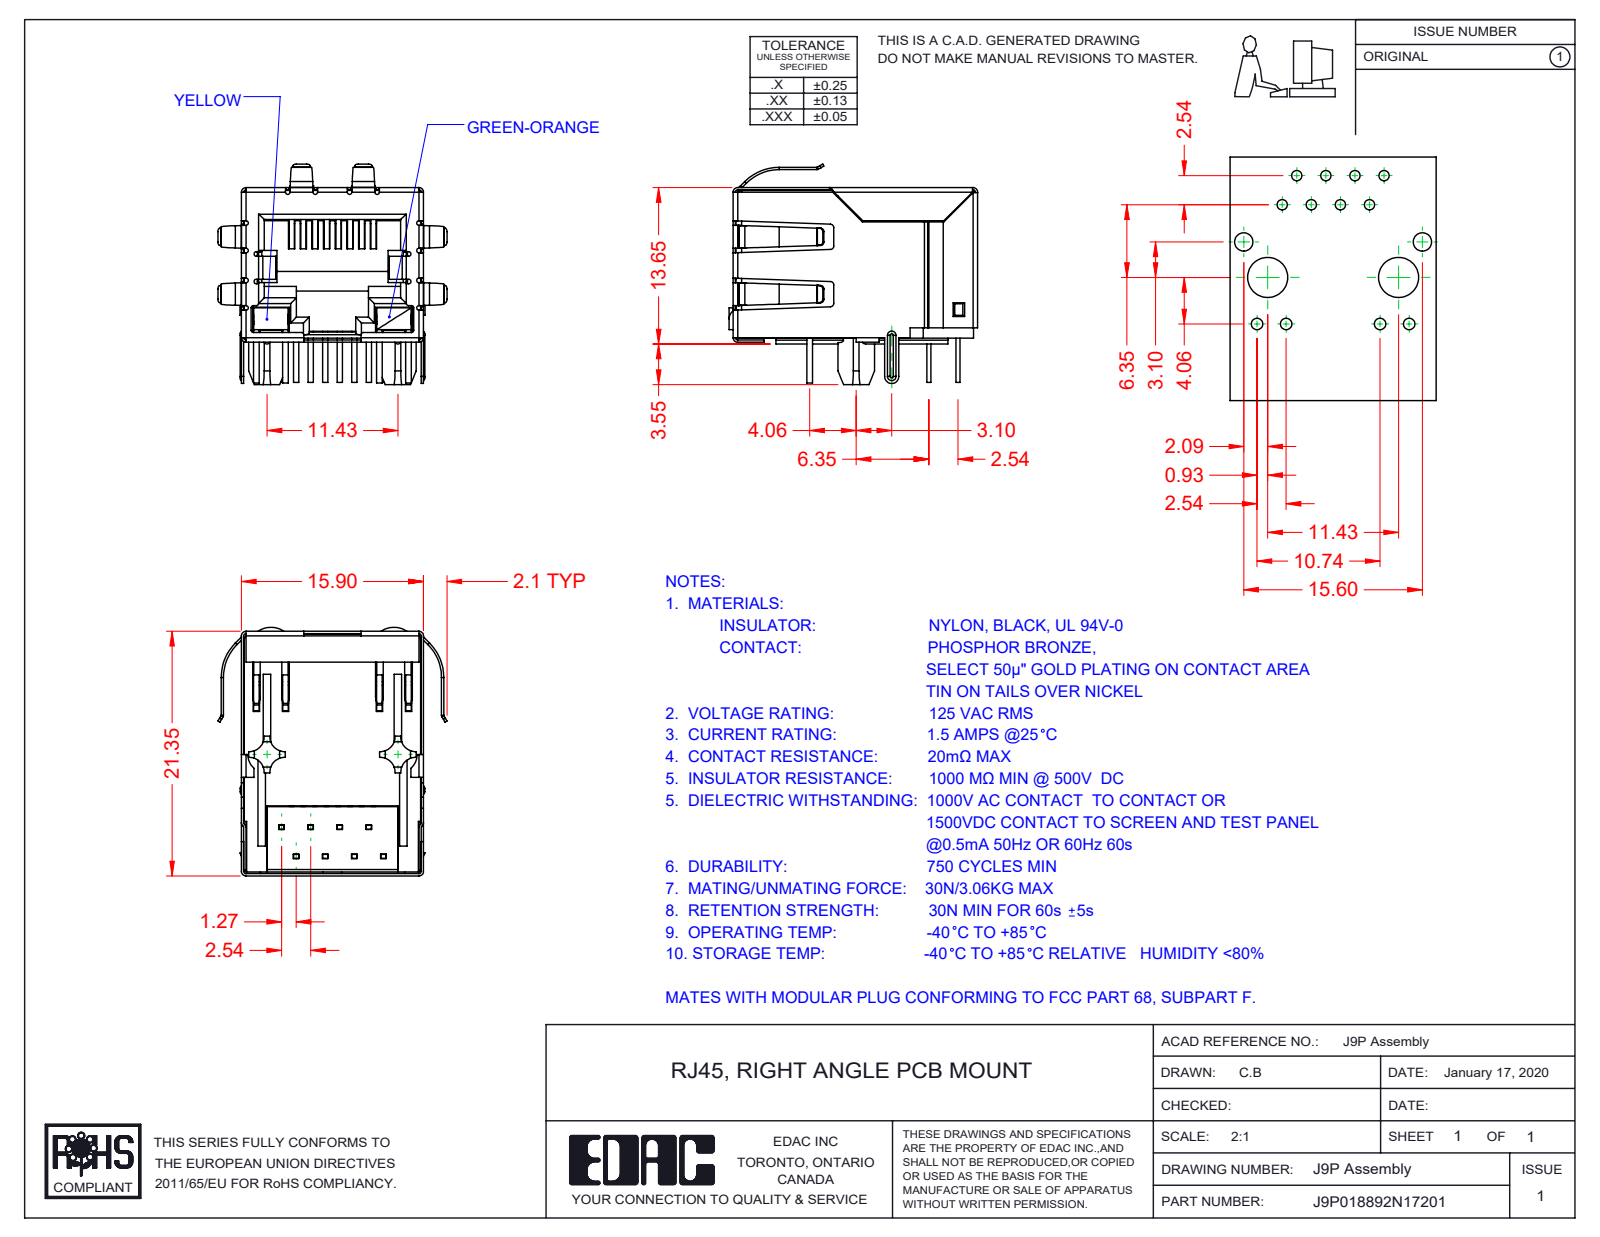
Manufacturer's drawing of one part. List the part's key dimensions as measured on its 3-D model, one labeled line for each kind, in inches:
Part name (STEP PRODUCT): 9P-LED LED LH_1-Yellow; 9P-LED Insulator; J9P018892N17202; 9P-LED Contacts (+4 more)
STEP written by: SolidWorks 2016 (CONFIG_CONTROL_DESIGN)
Units: inches
Bodies: 13 solids, 1474 faces (1042 planar, 338 cylindrical, 94 other)
Overall size (bounding box): 0.854 × 0.787 × 0.758
Volume: 0.164 in³ · Surface area: 11.65 in²
Partial cylindrical surfaces — rounded edges, fillets, slot ends (radius × count): R0.008 ×39, R0.02 ×22, R0.012 ×20, R0.016 ×16, R0.051 ×8, R0.009 ×5, R0.004 ×4, R0.012 ×4
Main face-to-face distances: 0.608, 0.618, 0.616, 0.014, 0.021, 0.61, 0.487, 0.024, 0.055, 0.023
